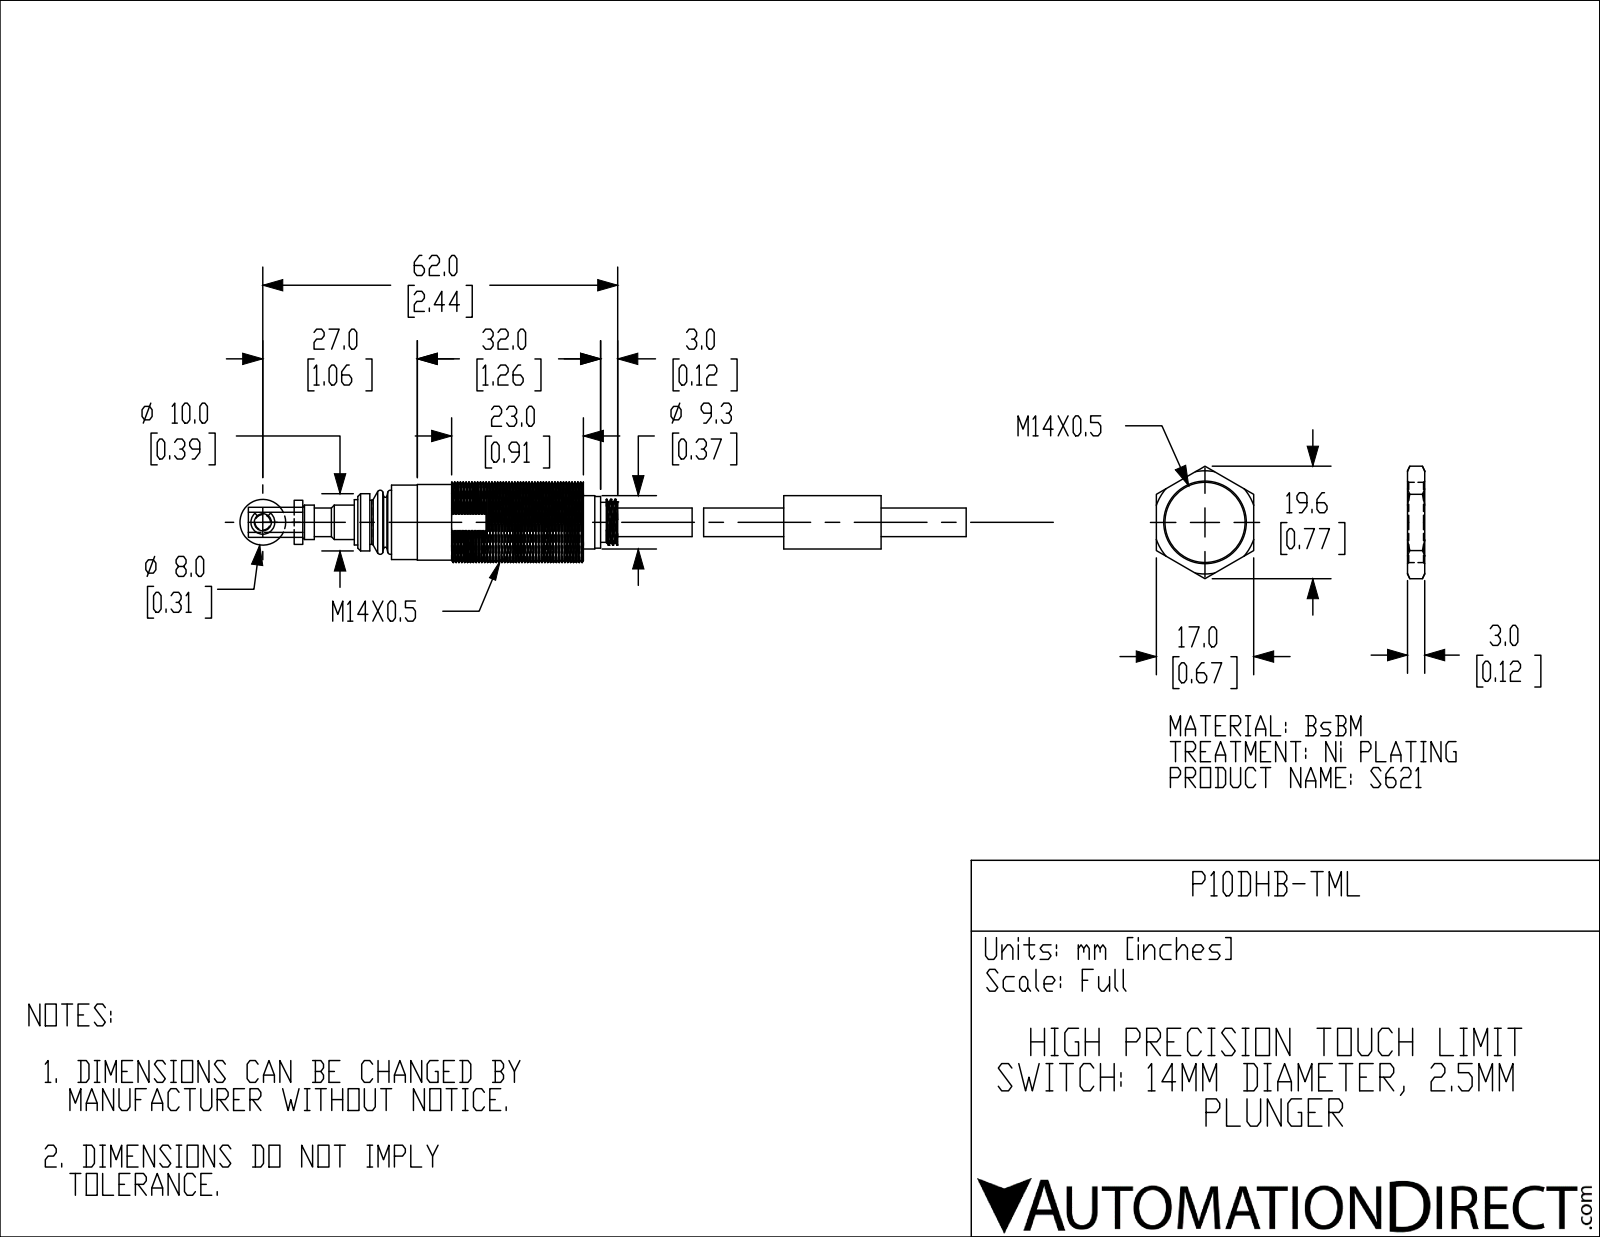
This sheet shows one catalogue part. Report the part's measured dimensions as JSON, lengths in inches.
{"part_name": "P10DHB-TML", "step_written_by": "SolidWorks 2018 (AUTOMOTIVE_DESIGN)", "units": "inches", "bodies": {"solids": 2, "faces": 105, "planar": 62, "cylindrical": 28, "other": 15}, "overall_size": [4.995, 0.551, 0.551], "volume_in3": 0.509, "surface_area_in2": 6.436, "round_bosses_or_shafts": [[0.315, 2], [0.551, 1], [0.52, 1], [0.512, 1], [0.394, 1], [0.366, 1], [0.354, 1], [0.311, 1]], "partial_cylinders_radius": [[0.082, 1]], "face_to_face_distances": [0.118, 0.197, 0.079, 0.669, 0.315, 0.12, 2.047, 0.199, 0.195, 0.317]}
